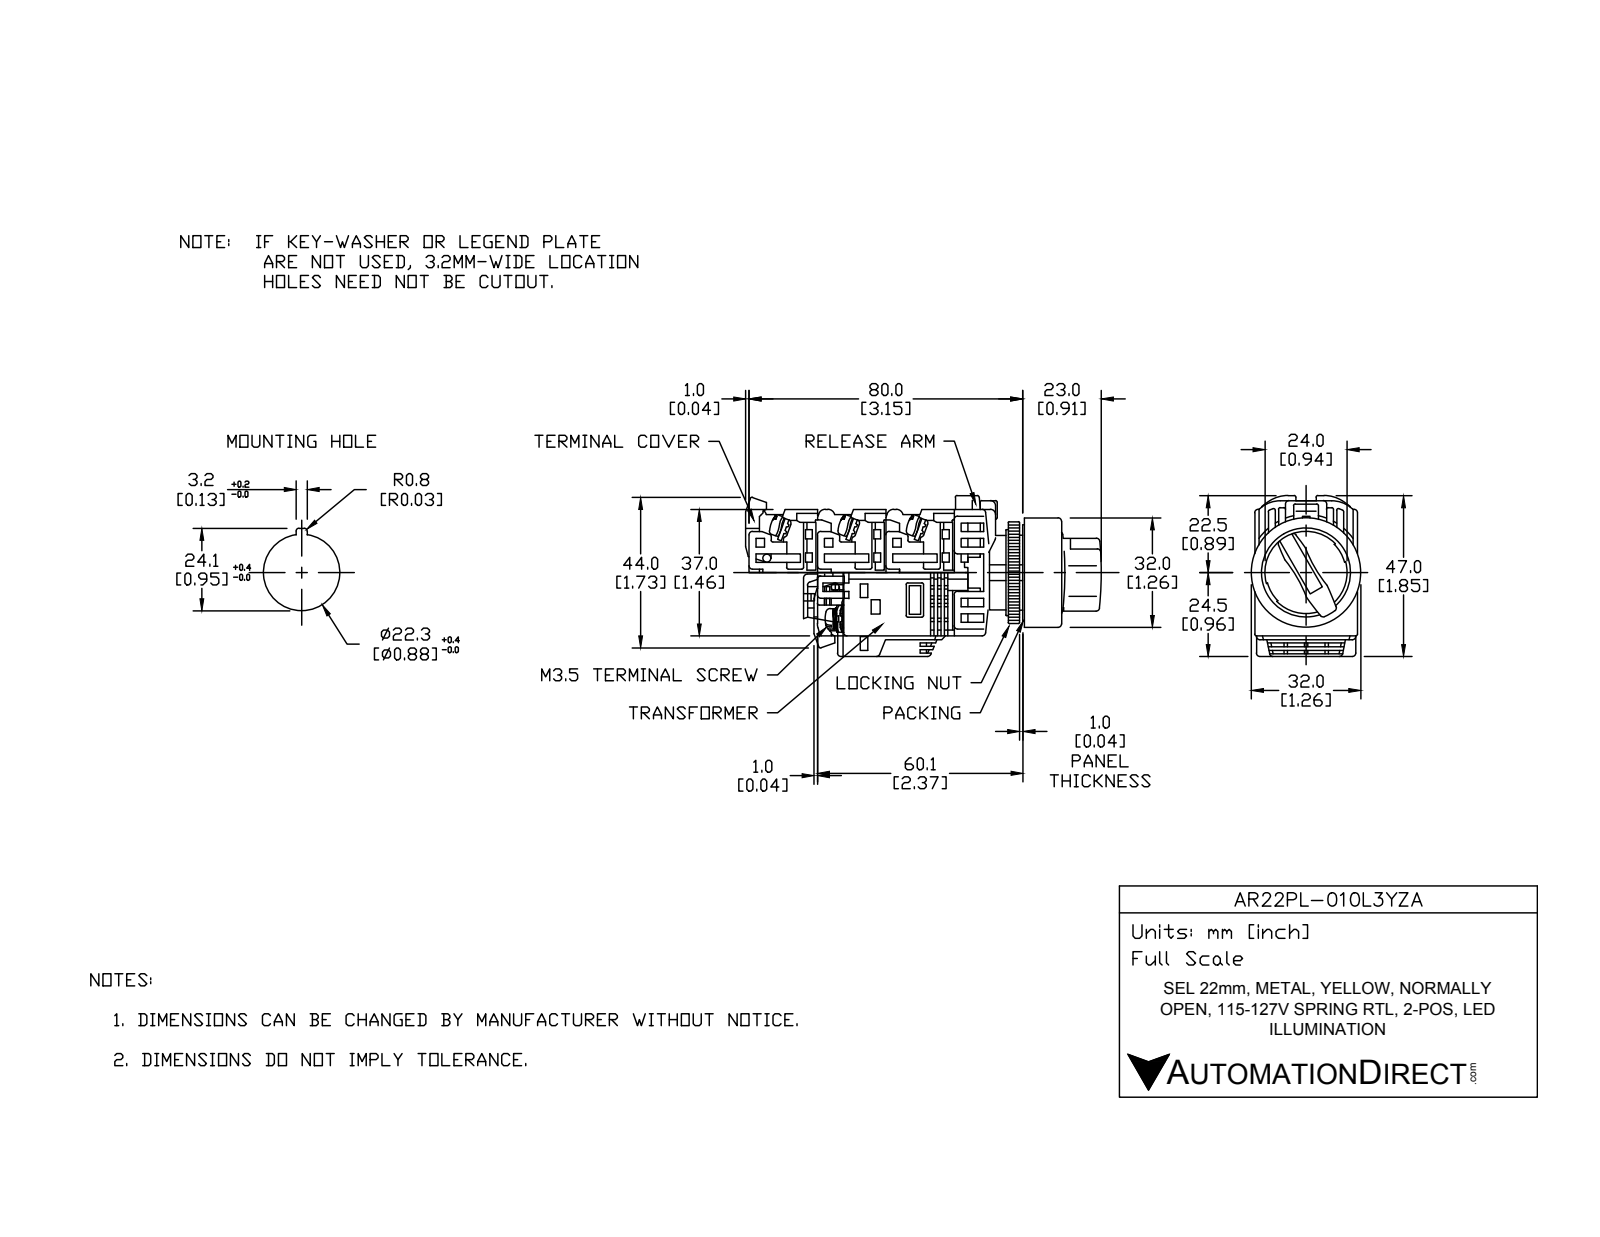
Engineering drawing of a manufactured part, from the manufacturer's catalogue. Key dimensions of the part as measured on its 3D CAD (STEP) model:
Part name (STEP PRODUCT): AR22PL-010L3YZA
STEP written by: SolidWorks 2017 (AUTOMOTIVE_DESIGN)
Units: millimetres
Bodies: 18 solids, 462 faces (317 planar, 118 cylindrical, 27 other)
Overall size (bounding box): 84.5 × 43.81 × 32
Volume: 48 971 mm³ · Surface area: 26 711 mm²
Round holes (diameter × count): ⌀21.8 ×1, ⌀22 ×1, ⌀25 ×1, ⌀31 ×1
Round bosses / shafts (diameter × count): ⌀5 ×4, ⌀32 ×1, ⌀30.5 ×1, ⌀29.8 ×1, ⌀24 ×1, ⌀21.75 ×1, ⌀17 ×1
Partial cylindrical surfaces — rounded edges, fillets, slot ends (radius × count): R0.5 ×39, R1.75 ×8, R1 ×6, R5 ×4, R4 ×2, R12 ×1, R16.59 ×1, R17.59 ×1
Main face-to-face distances: 1, 18, 29, 20, 3, 28.5, 0.5, 2, 21, 10
